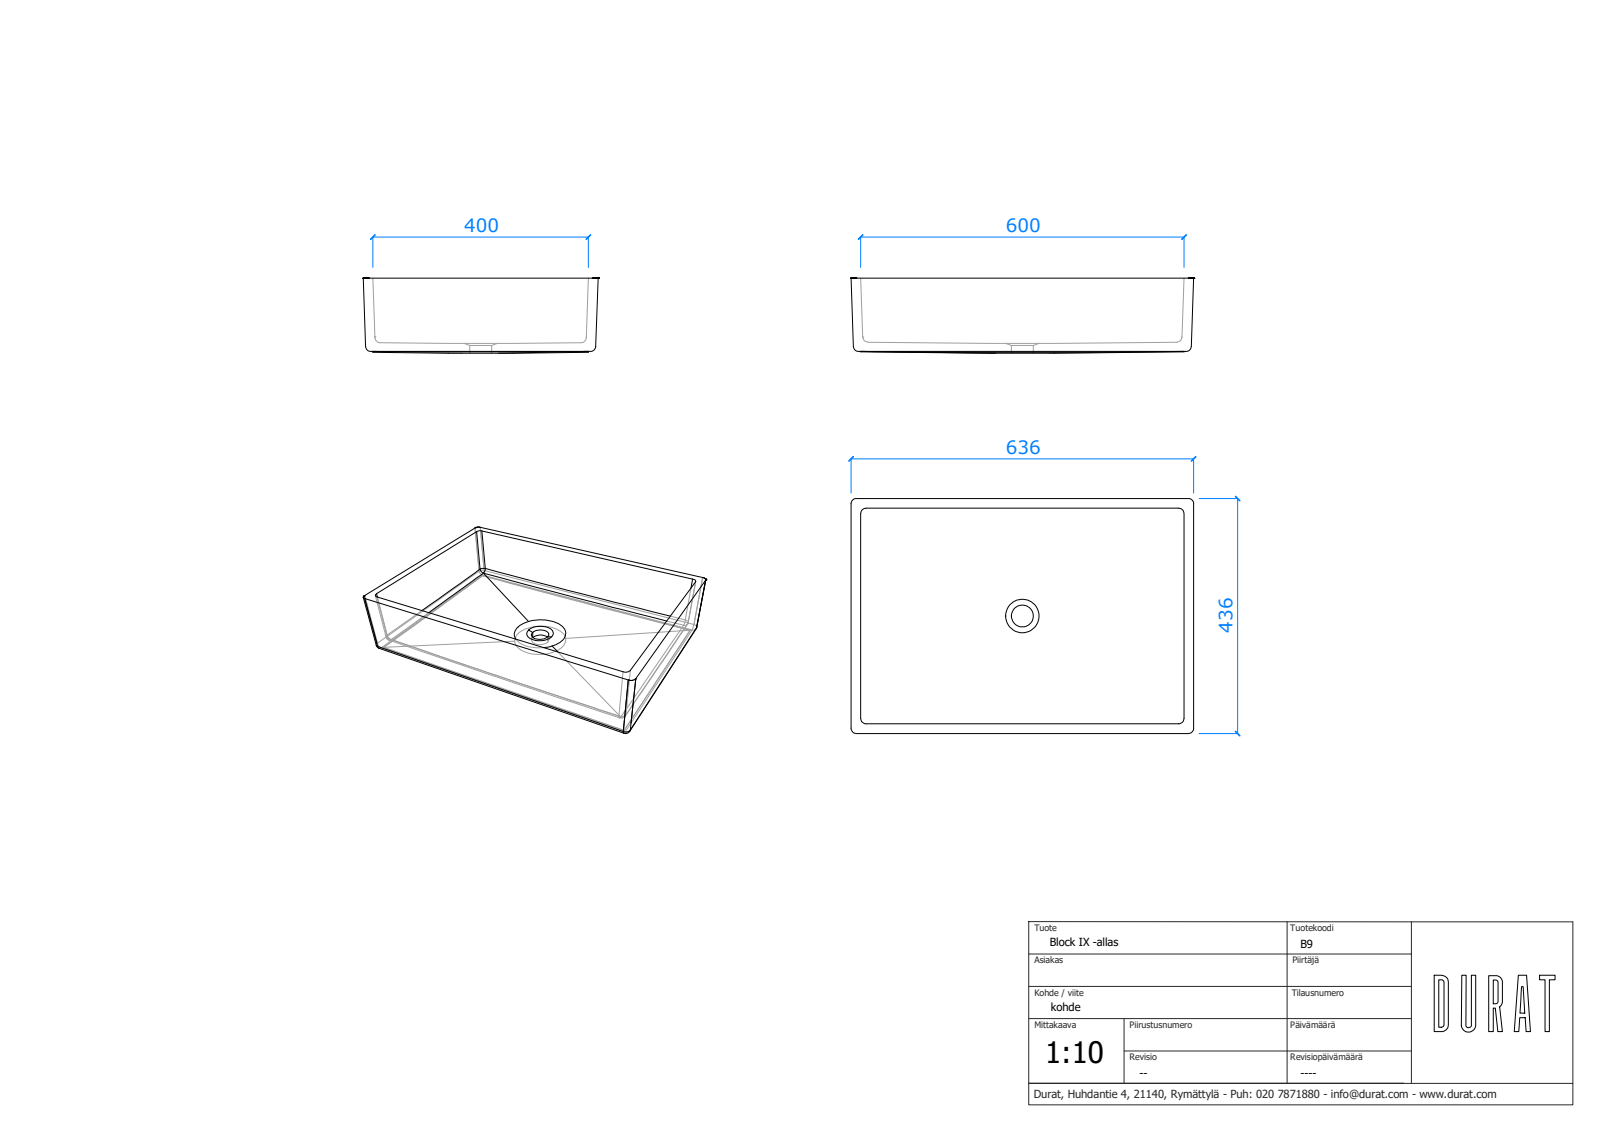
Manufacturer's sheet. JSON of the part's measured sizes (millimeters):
{"step_written_by": "ST-DEVELOPER v15 (AUTOMOTIVE_DESIGN)", "units": "millimeters", "bodies": {"solids": 0, "faces": 48, "planar": 16, "cylindrical": 0, "other": 32}, "overall_size": [636.02, 436.02, 139.2], "face_to_face_distances": [18.01, 17.98, 139.2, 18, 121.2, 3.2, 14.8, 136, 400, 600]}
